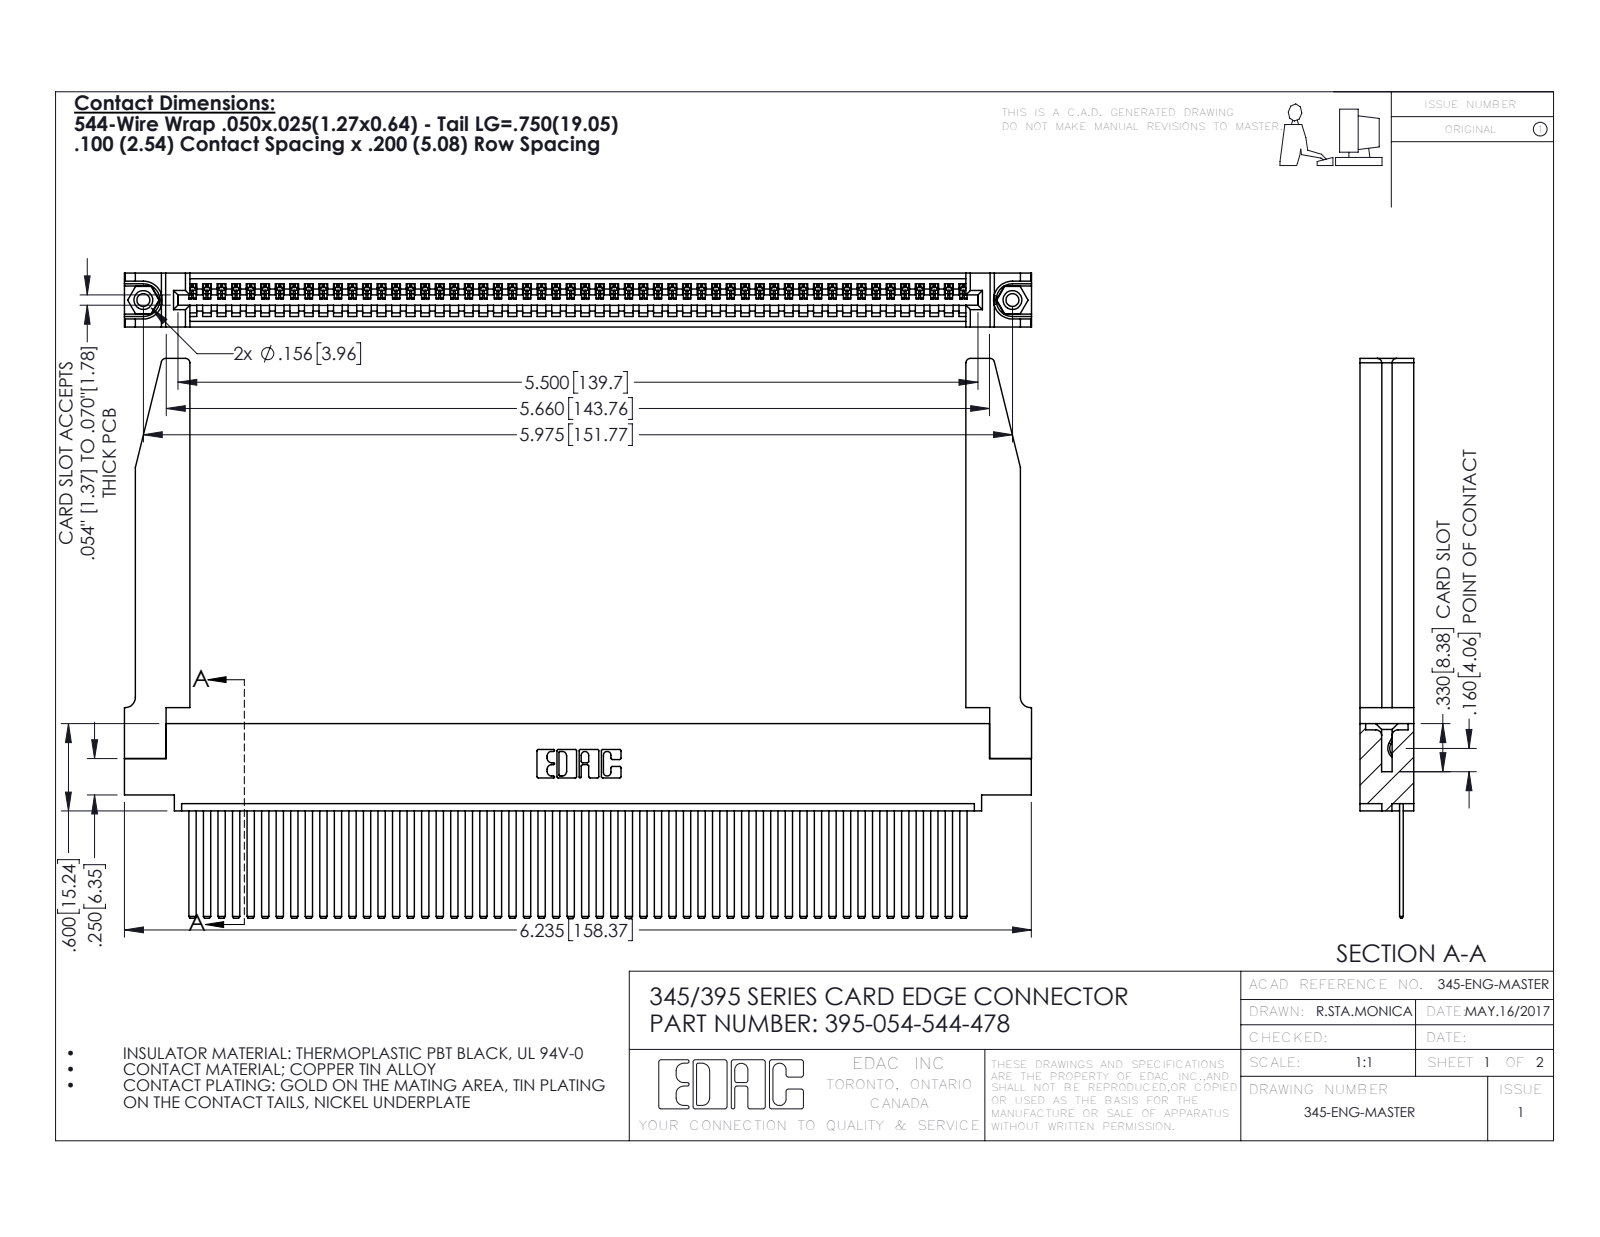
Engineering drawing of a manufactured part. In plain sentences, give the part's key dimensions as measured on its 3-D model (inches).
The part is named "345-292-001_345-293-144; 345-220-078_345-220-078; 345 Part_0.110 Offset - 0.156 Dia-TH; 395-054-544-478 (+1 more)". Its 3-D file was written by "SolidWorks 2016 (CONFIG_CONTROL_DESIGN)". It is 59 solids with 3172 faces: 2170 planar, 950 cylindrical and 52 other. Overall it measures 6.236 by 3.847 by 0.37 inches. Its volume is 1.432 cubic inches and its surface area 46.23 square inches. Round holes: 2 of diameter 0.089, 2 of diameter 0.125, 2 of diameter 0.156, 1 of diameter 0.064. Round bosses or shafts: 2 of diameter 0.155. Partial cylindrical surfaces (rounded edges, fillets, slot ends): 108 of radius 0.006, 22 of radius 0.01, 8 of radius 0.03, 6 of radius 0.007, 6 of radius 0.031, 3 of radius 0.026, 2 of radius 0.031, 2 of radius 0.04. The main face-to-face distances are 0.072, 0.298, 0.37, 0.098, 0.272, 0.025, 0.2, 0.225, 0.148, 0.15. The hole center spacings are 0.27, 5.739, 5.975.
